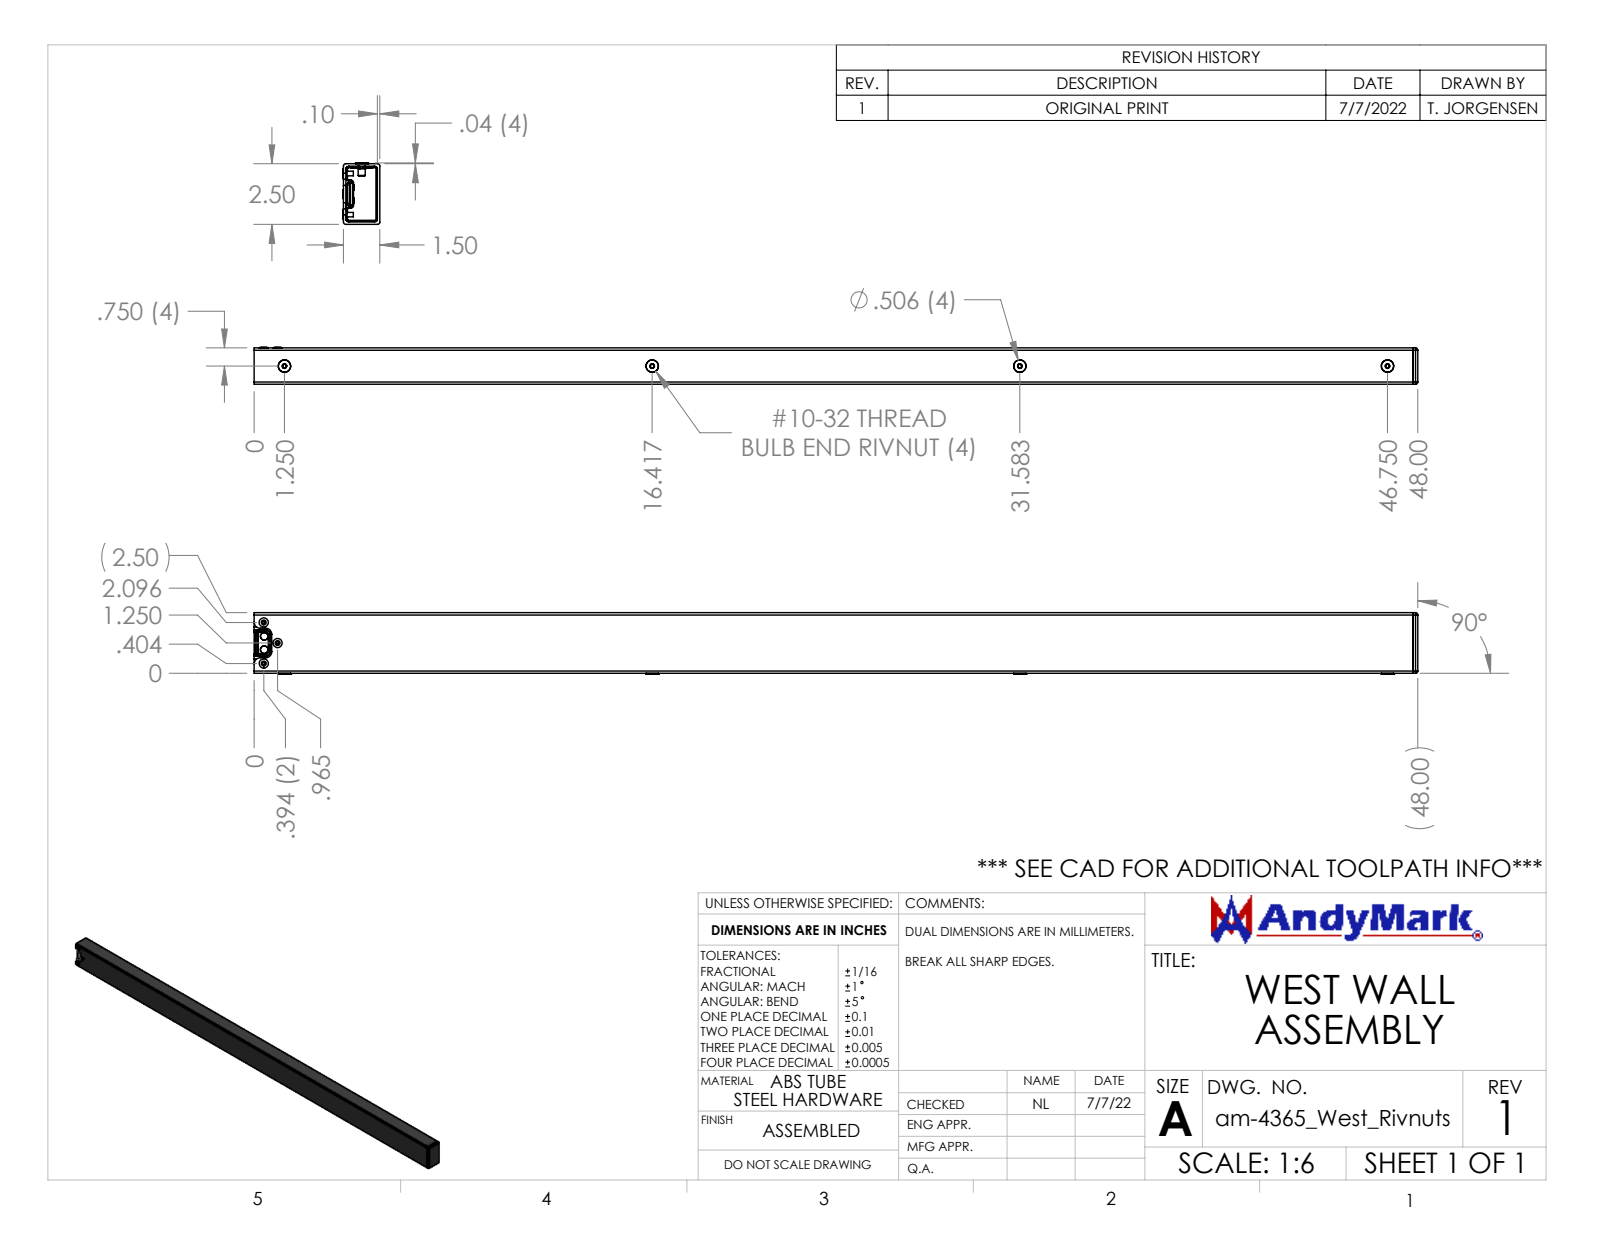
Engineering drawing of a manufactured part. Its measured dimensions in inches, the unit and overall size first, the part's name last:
Units: inches
Overall size (bounding box): 48 × 2.538 × 1.531
Round holes (diameter × count): ⌀0.19 ×4, ⌀0.339 ×4, ⌀0.1 ×3, ⌀0.201 ×3, ⌀0.205 ×3, ⌀0.165 ×2
Round bosses / shafts (diameter × count): ⌀0.51 ×4, ⌀0.358 ×4, ⌀0.296 ×4, ⌀0.375 ×3, ⌀0.187 ×3, ⌀0.315 ×2, ⌀0.157 ×2
Partial cylindrical surfaces — rounded edges, fillets, slot ends (radius × count): R0.004 ×12, R0.094 ×8, R0.071 ×6, R0.118 ×6, R0.125 ×4, R0.25 ×4, R0.028 ×2, R0.079 ×2
Main face-to-face distances: 0.1, 1.4, 1.5, 2.4, 1.3, 2.5, 2.3, 0.065, 0.165, 0.2
Hole centre spacings: 0.571, 0.616, 0.617, 1.021, 1.021, 1.122, 15.167, 30.333
Volume: 37.74 in³ · Surface area: 745.8 in²
Bodies: 13 solids, 701 faces (244 planar, 237 cylindrical, 220 other)
Part name (STEP PRODUCT): Tube plug End Cap; am-1577 10-32 RivNut for Plastics_Installed; L903-7336 v5 v4_14; L903-7336 v5 v4_2 (+6 more)
STEP written by: SolidWorks 2022 (CONFIG_CONTROL_DESIGN)
